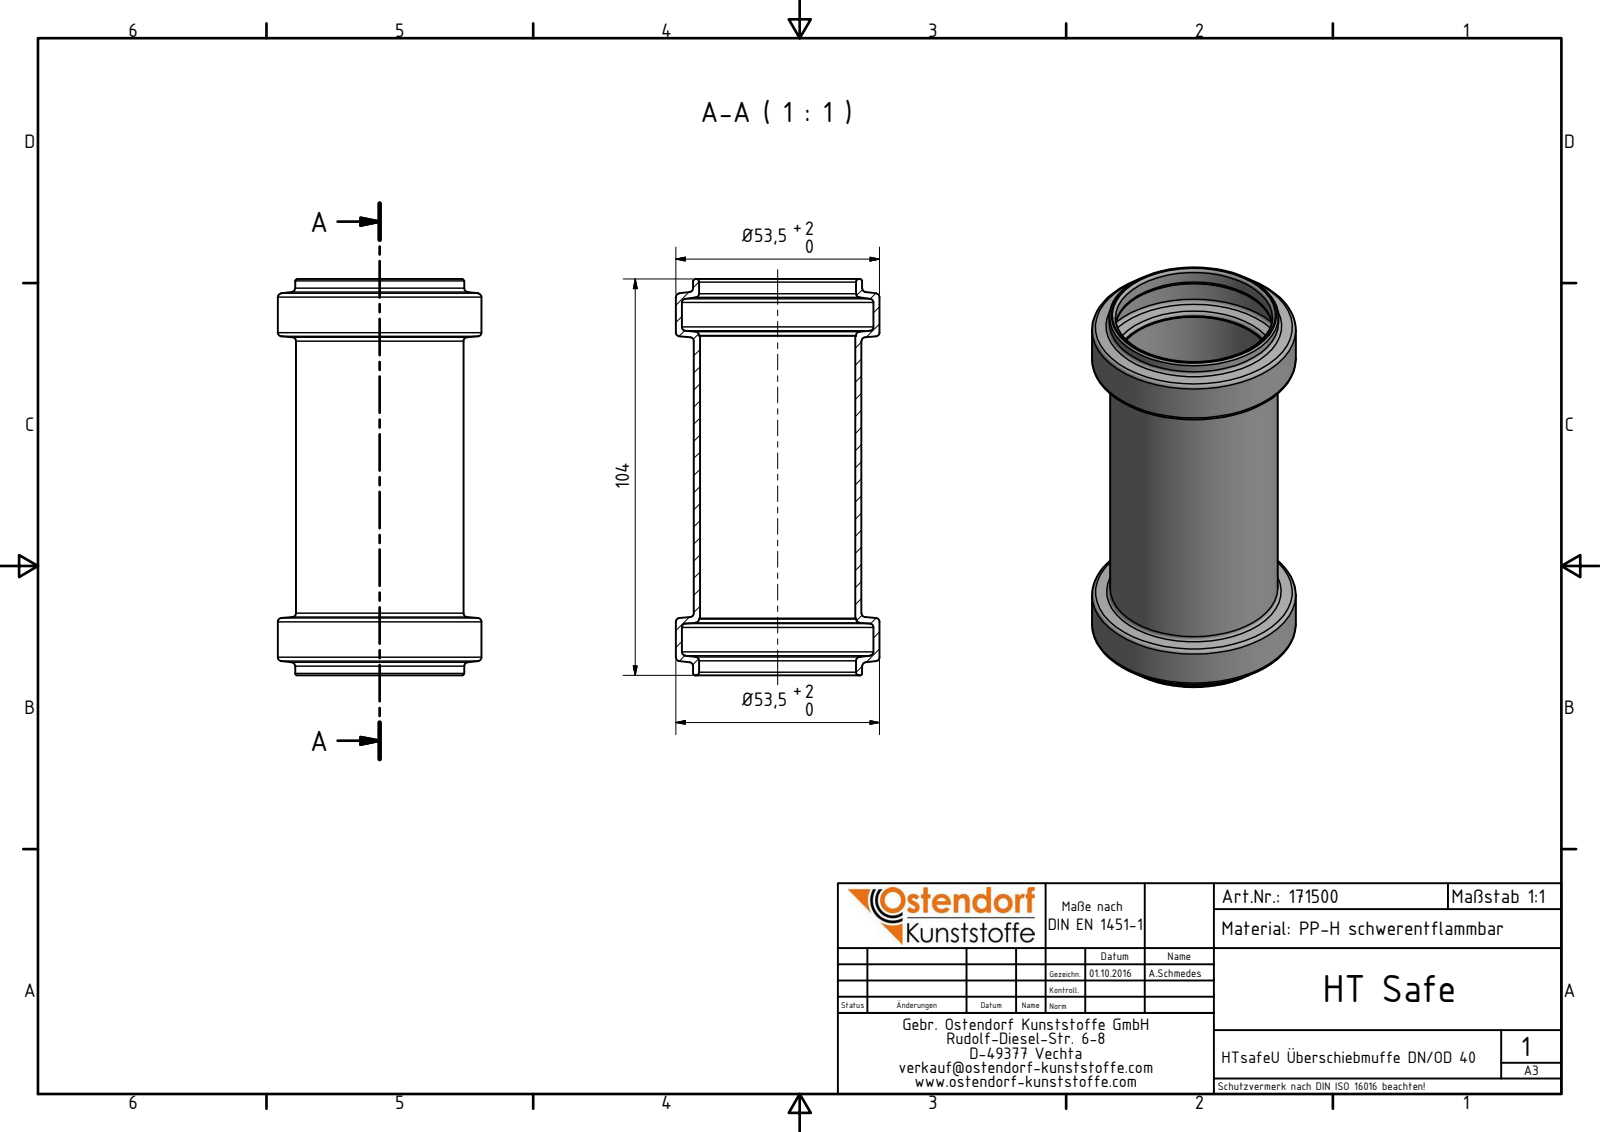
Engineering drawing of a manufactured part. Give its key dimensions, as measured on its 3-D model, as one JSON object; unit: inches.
{"part_name": "171500 HTsafeU DN_OD 40", "step_written_by": "Autodesk Inventor 2016 (AUTOMOTIVE_DESIGN)", "units": "inches", "bodies": {"solids": 1, "faces": 44, "planar": 4, "cylindrical": 12, "other": 28}, "overall_size": [4.094, 2.106, 2.106], "volume_in3": 1.649, "surface_area_in2": 51.78, "round_holes": [[1.606, 1], [1.622, 1], [1.98, 1]], "round_bosses_or_shafts": [[2.106, 1], [1.748, 1], [1.732, 1]], "face_to_face_distances": [0.587, 3.508, 4.094, 2.921]}
